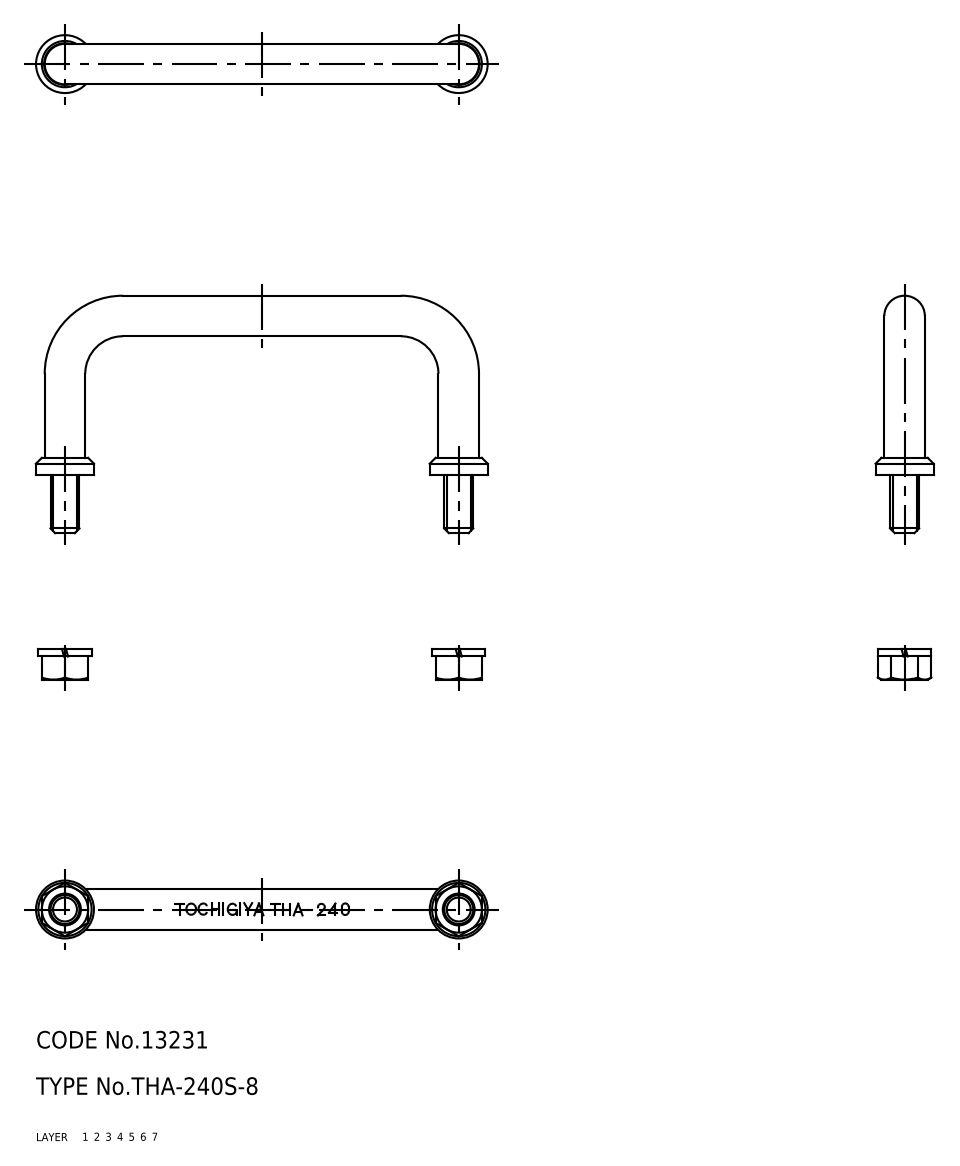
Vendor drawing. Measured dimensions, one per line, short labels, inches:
name: facing ring; nut; washer; THA_240S_8 (+1 more)
written by: SolidWorks 2015 (AUTOMOTIVE_DESIGN)
unit: in
bodies: 7 solids, 90 faces (30 planar, 34 cylindrical, 26 other)
size: 3.071 × 1.614 × 0.394
volume: 0.329 in³; area: 6.448 in²
holes: 2× ⌀0.197, 2× ⌀0.217, 2× ⌀0.283
bosses: 3× ⌀0.276, 2× ⌀0.394, 2× ⌀0.362
face distances: 0.315, 0.079, 0.13, 0.051, 0.118, 1.339, 0.169, 0.039, 0.157, 0.209
hole spacings: 2.677
